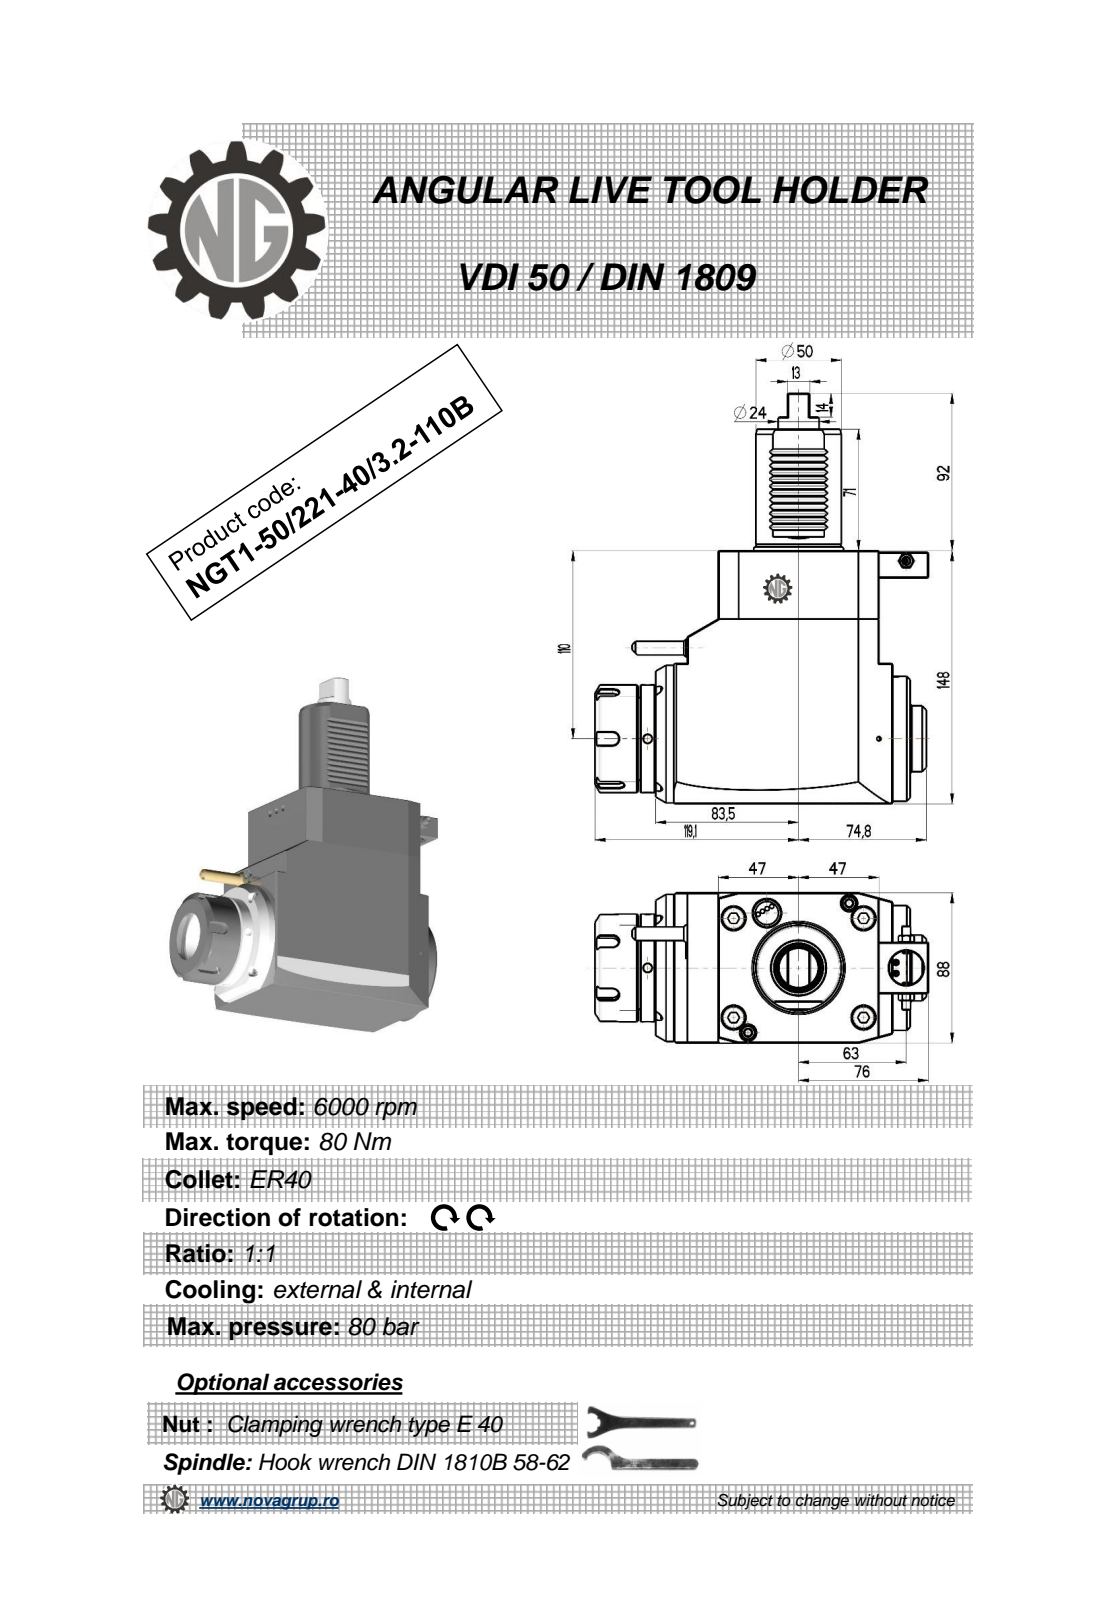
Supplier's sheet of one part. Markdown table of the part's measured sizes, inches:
| quantity | value |
| --- | --- |
| part name | NGT1_50_221_40_3_2_110B |
| STEP written by | PRO/ENGINEER BY PARAMETRIC TECHNOLOGY CORPORATION, 2010280 (CONFIG_CONTROL_DESIGN) |
| units | inches |
| bodies | 1 solid, 437 faces (210 planar, 102 cylindrical, 125 other) |
| overall size | 9.449 × 7.681 × 3.465 |
| volume | 112.5 in³ |
| surface area | 178.8 in² |
| round holes (diameter × count) | 0.197 × 3, 0.15 × 2, 0.157 × 2, 0.118 × 1, 0.374 × 1, 0.787 × 1, 1.319 × 1 |
| round bosses / shafts (diameter × count) | 3.386 × 1, 2.874 × 1, 2.48 × 1, 2.008 × 1, 1.969 × 1, 1.575 × 1, 1.516 × 1, 0.945 × 1 |
| partial cylindrical surfaces (radius × count) | 0.01 × 12, 0.012 × 12, 0.008 × 6, 0.148 × 5, 0.031 × 2 |
| main face-to-face distances | 3.465, 5.827, 0.315, 3.701, 1.437, 5.138, 4.724, 5.858, 4.421, 0.72 |
| hole center spacings | 0.354, 4.012, 0.709, 1.958, 2.065, 2.225, 2.23, 3.996 |
